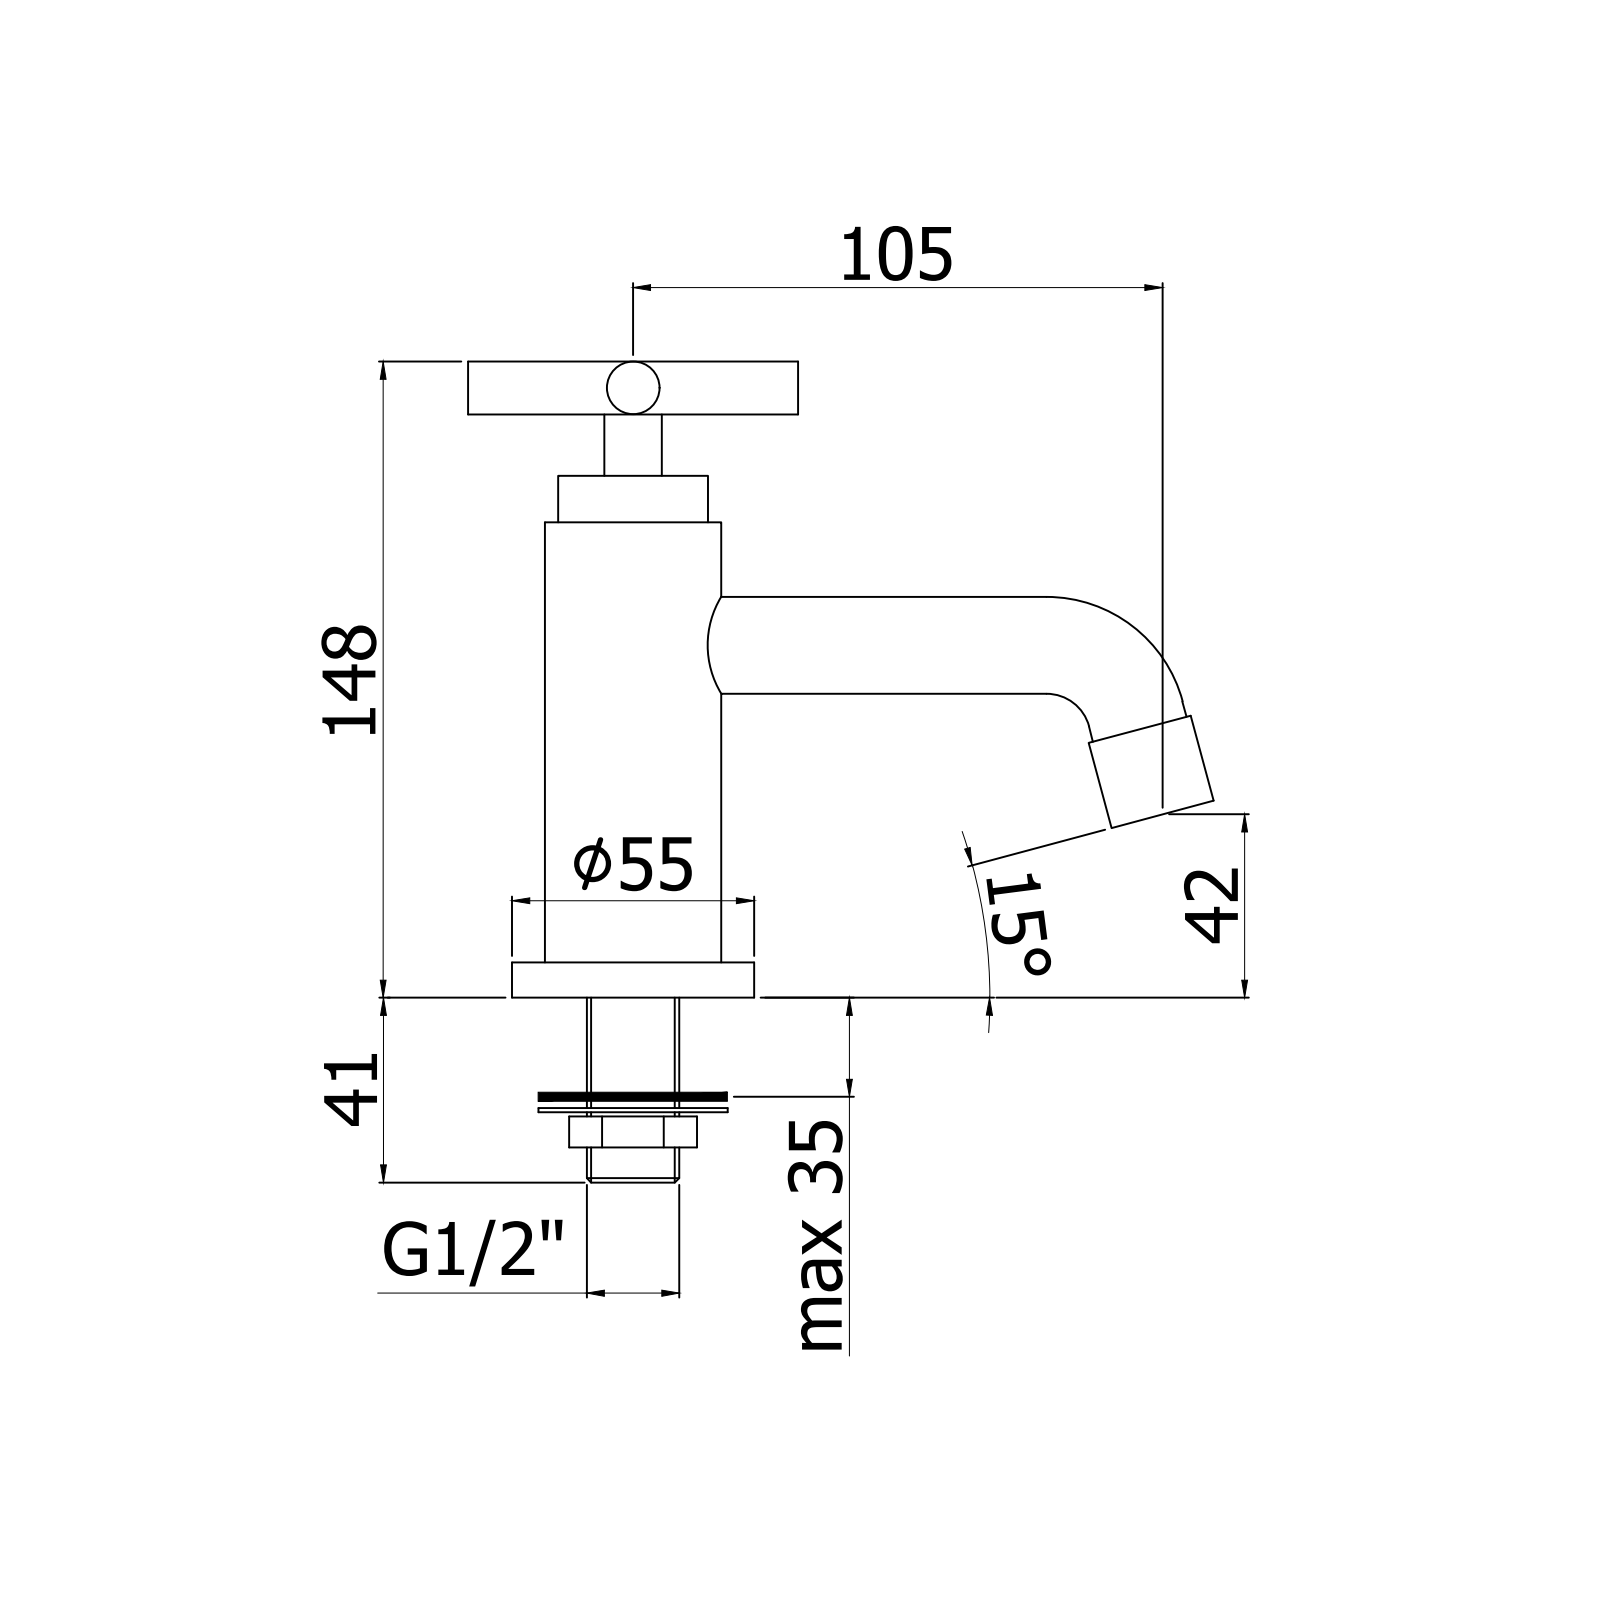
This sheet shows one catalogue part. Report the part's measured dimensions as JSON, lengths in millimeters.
{"part_name": "QTV090CR", "step_written_by": "CREO PARAMETRIC BY PTC INC, 2020044 (CONFIG_CONTROL_DESIGN)", "units": "millimeters", "bodies": {"solids": 4, "faces": 1858, "planar": 1618, "cylindrical": 137, "other": 103}, "overall_size": [153.7, 148.7, 75], "volume_mm3": 165832, "surface_area_mm2": 57559, "round_holes": [[10, 2], [19, 2], [3.3, 1], [4.5, 1], [7, 1], [8, 1], [8.8, 1], [9.5, 1], [10.3, 1], [13.5, 1], [16, 1], [16.3, 1]], "round_bosses_or_shafts": [[22, 2], [12, 2], [55, 1], [49, 1], [39.7, 1], [36, 1], [34, 1], [24, 1]], "partial_cylinders_radius": [[0.1, 17], [0.5, 2], [1, 2], [3, 1], [9.4, 1]], "face_to_face_distances": [4, 5, 2, 11, 112, 6, 123, 9, 118, 114]}
